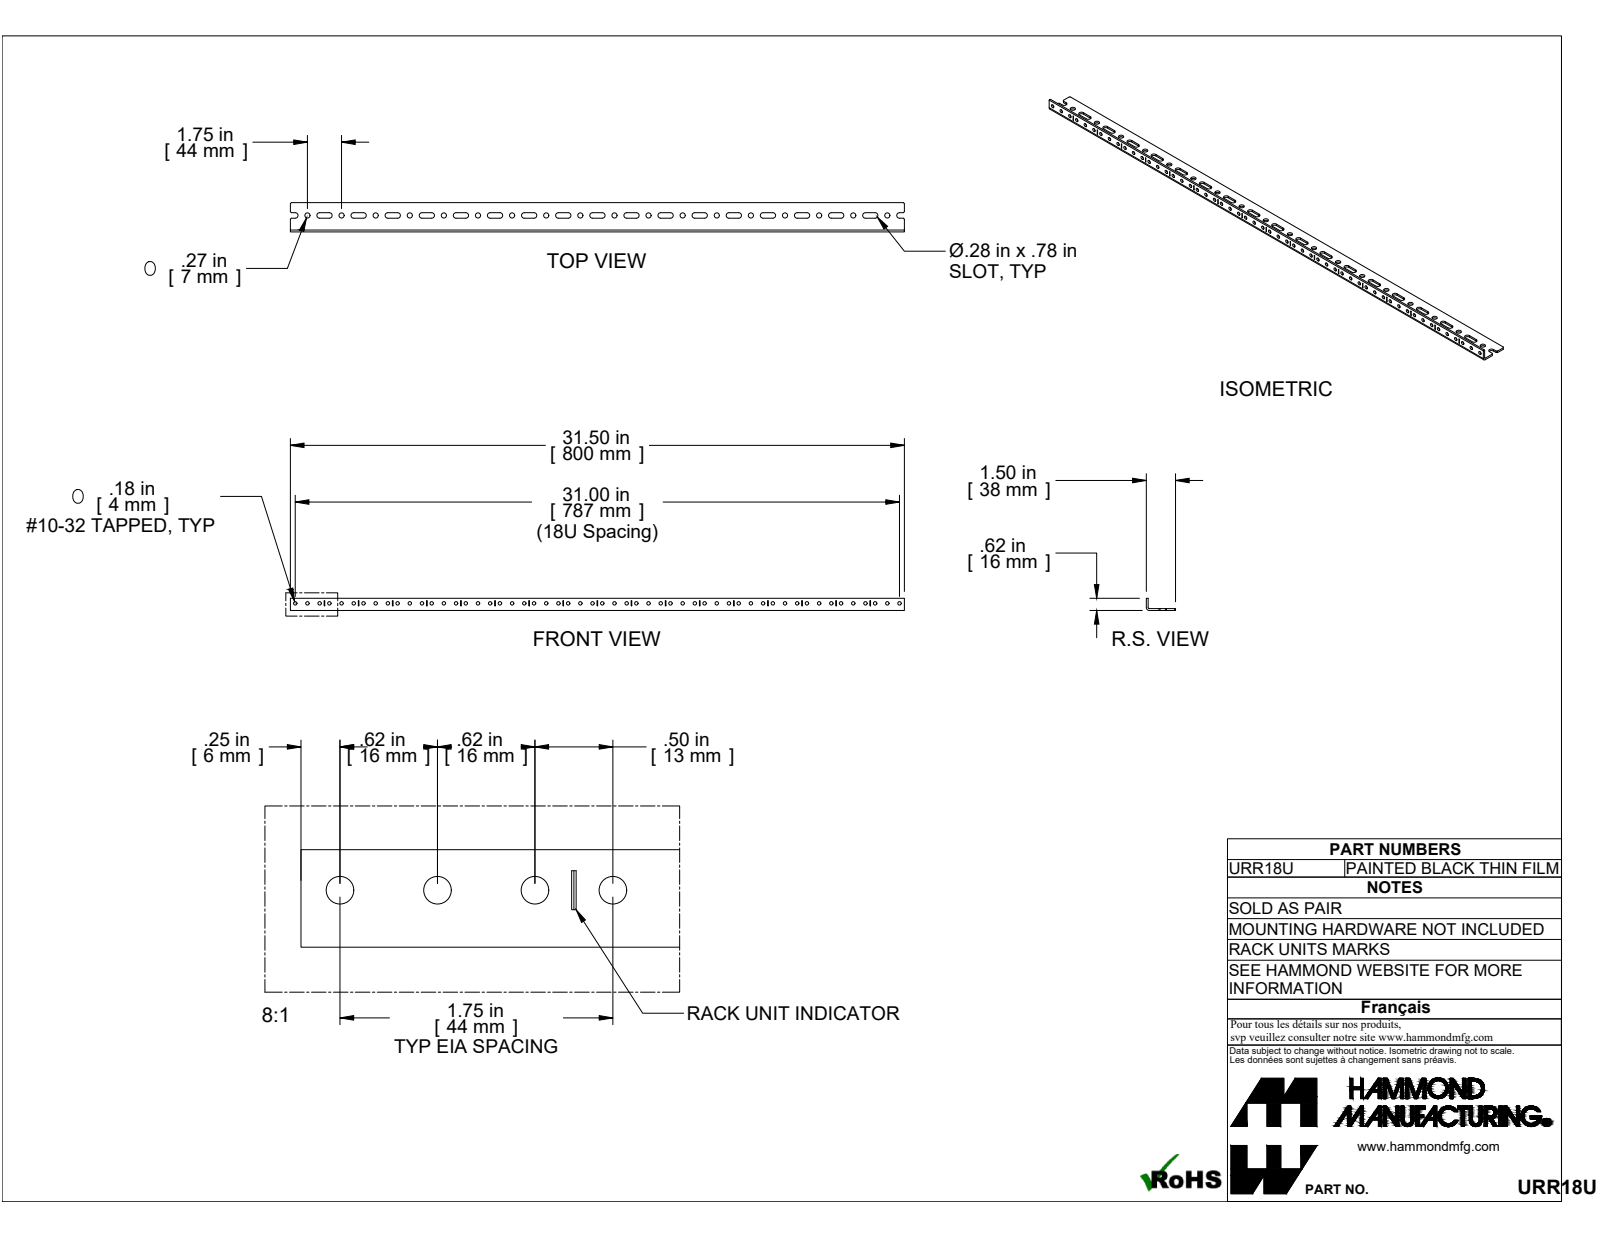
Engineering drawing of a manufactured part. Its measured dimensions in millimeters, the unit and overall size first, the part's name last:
Units: millimetres
Overall size (bounding box): 800.1 × 38.1 × 15.88
Round holes (diameter × count): ⌀4.5 ×54, ⌀6.76 ×18
Partial cylindrical surfaces — rounded edges, fillets, slot ends (radius × count): R3.57 ×36, R1.22 ×1, R3.63 ×1
Main face-to-face distances: 2.41, 15.88, 13.47, 38.1, 35.69, 17.84, 24.98, 15.43, 22.57, 7.14
Hole centre spacings: 88.9, 44.45, 133.35, 177.8, 266.7, 311.15, 222.25, 15.87
Volume: 88 200 mm³ · Surface area: 82 111 mm²
Bodies: 1 solid, 232 faces (122 planar, 110 cylindrical, 0 other)
Part name (STEP PRODUCT): COM57213-18
STEP written by: ST-DEVELOPER v16.7 (AUTOMOTIVE_DESIGN)
